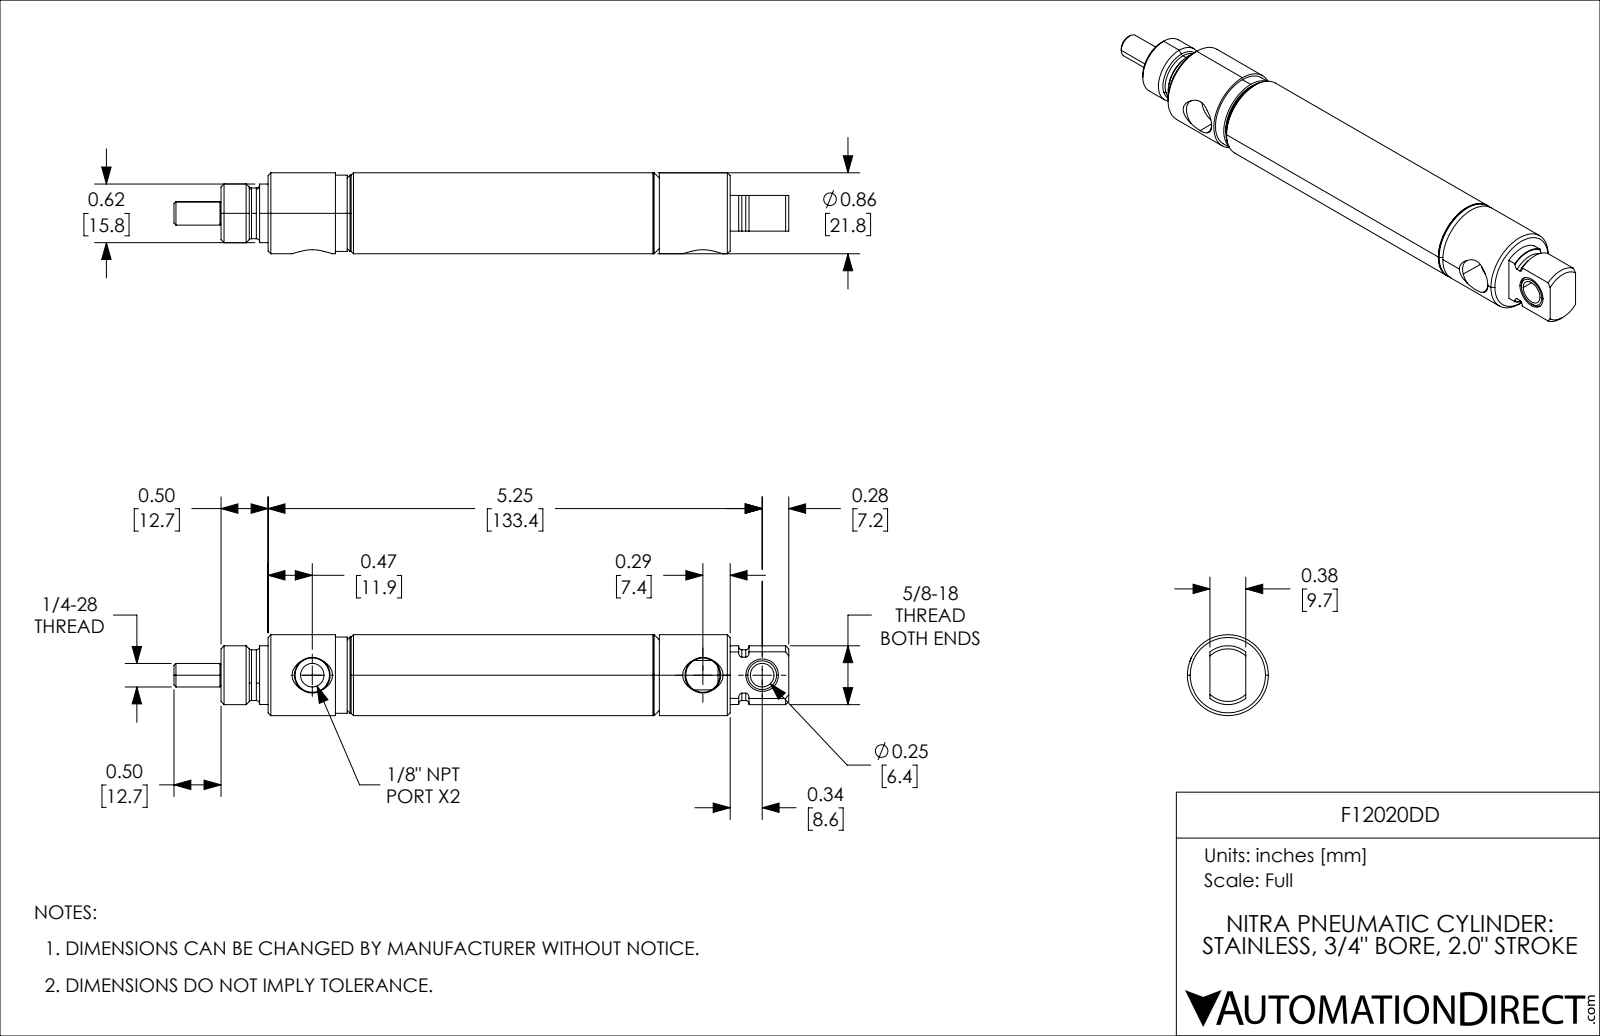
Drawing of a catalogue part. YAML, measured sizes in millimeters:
part_name: "F12020DD_7; F12020DD_11; F12020DD_3; F12020DD_5 (+2 more)"
step_written_by: "SolidWorks 2021 (CONFIG_CONTROL_DESIGN)"
units: millimeters
bodies: {solids: 5, faces: 158, planar: 29, cylindrical: 61, other: 68}
overall_size: [165.91, 21.84, 21.84]
volume: 34986
surface_area: 24025
round_holes:
  - {diameter: 6.35, count: 1}
  - {diameter: 6.38, count: 1}
  - {diameter: 6.95, count: 1}
  - {diameter: 7.92, count: 1}
  - {diameter: 8.78, count: 1}
  - {diameter: 9.23, count: 1}
  - {diameter: 12.7, count: 1}
  - {diameter: 17.83, count: 1}
round_bosses_or_shafts:
  - {diameter: 21.84, count: 1}
  - {diameter: 20.57, count: 1}
  - {diameter: 19.35, count: 1}
  - {diameter: 15.88, count: 1}
  - {diameter: 15.81, count: 1}
  - {diameter: 13.68, count: 1}
  - {diameter: 6.35, count: 1}
  - {diameter: 5.84, count: 1}
partial_cylinders:
  - {radius: 6.84, count: 1}
face_to_face_distances: [21.43, 40.49, 112.72, 50.8, 72.23, 96.92, 46.12, 24.69, 12.7, 9.66]
hole_center_spacings: [16, 105.41, 121.41]
